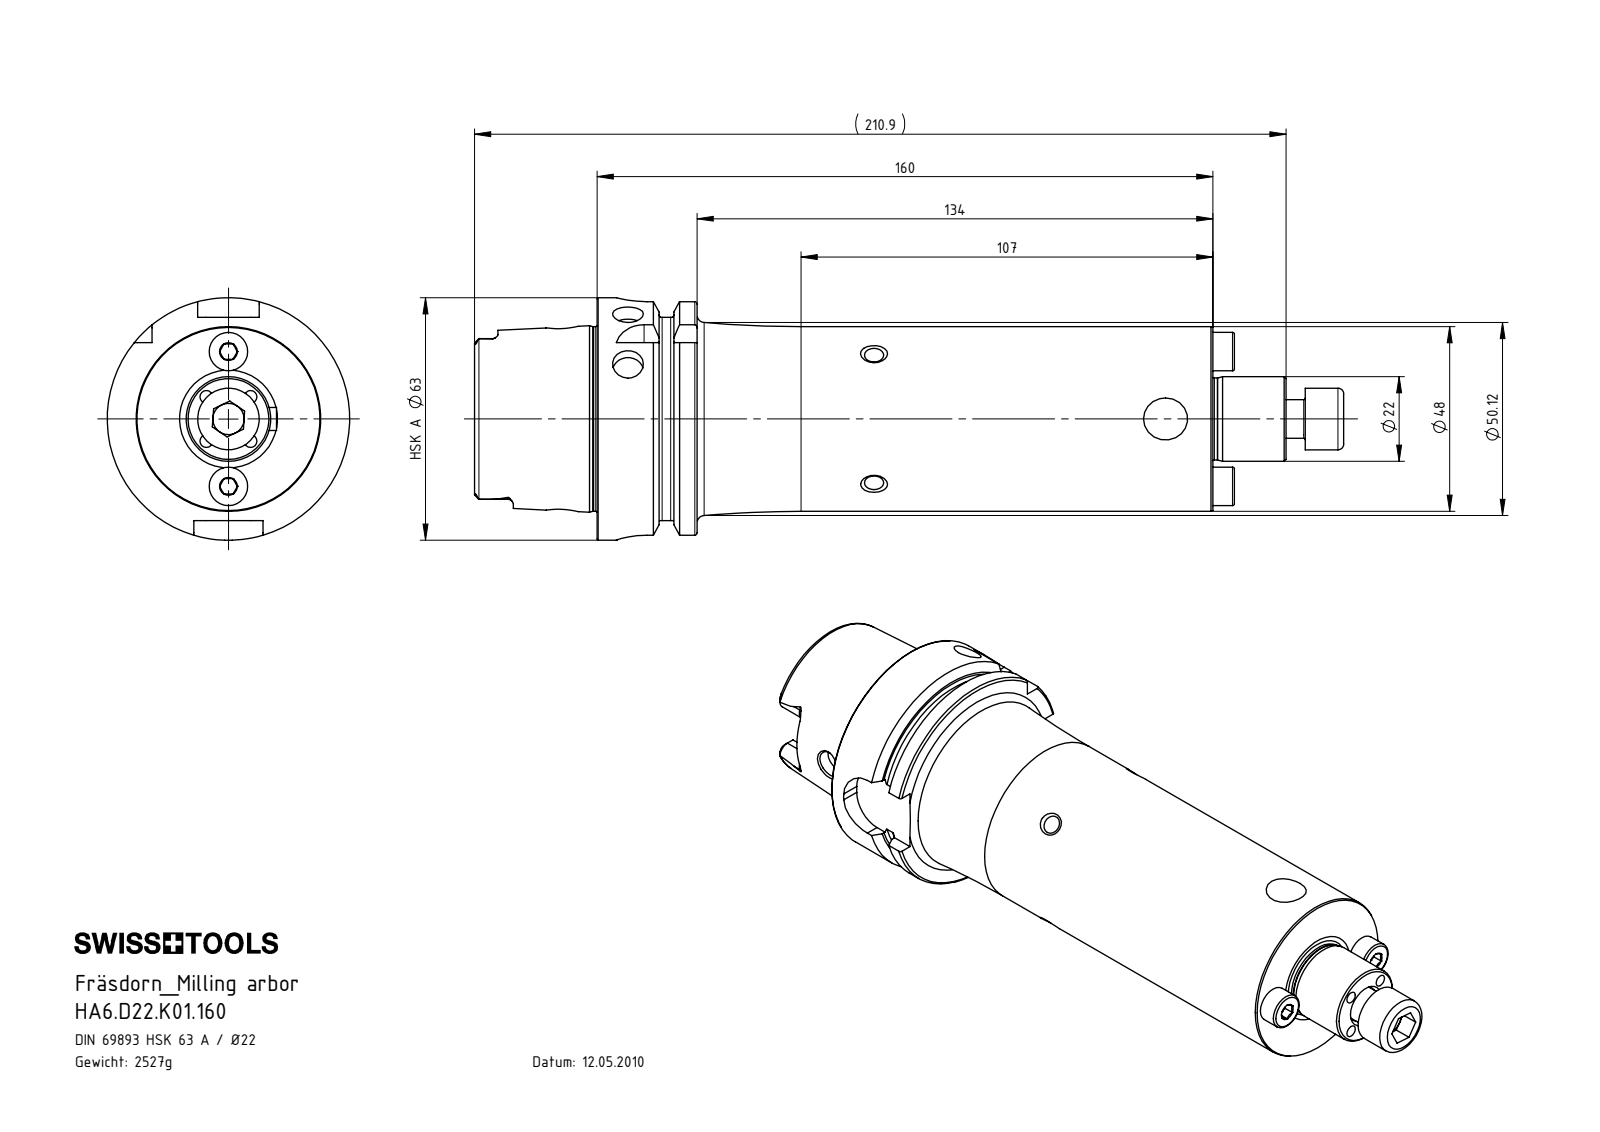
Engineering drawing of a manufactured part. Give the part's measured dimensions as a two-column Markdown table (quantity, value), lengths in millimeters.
| quantity | value |
| --- | --- |
| part name | DIN 6885 - 6x6x14; D22-ER2.001.017_B; HA6.D22.K01.160; ISO 4762 - M10 x 25 (+1 more) |
| STEP written by | SolidWorks 2017 (AUTOMOTIVE_DESIGN) |
| units | millimeters |
| bodies | 5 solids, 395 faces (96 planar, 116 cylindrical, 183 other) |
| overall size | 225.9 × 63 × 63 |
| volume | 325 069 mm³ |
| surface area | 54 256 mm² |
| round holes (diameter × count) | 3.3 × 6, 5 × 4, 8 × 4, 4.2 × 2, 7.5 × 1, 8.5 × 1, 10 × 1, 10.5 × 1, 17 × 1, 19 × 1, 34 × 1, 40 × 1 |
| round bosses / shafts (diameter × count) | 10 × 3, 5 × 2, 3.8 × 2, 63 × 1, 54.95 × 1, 48 × 1, 47.94 × 1, 22 × 1 |
| partial cylindrical surfaces (radius × count) | 1.4 × 6, 2.88 × 4, 3 × 4, 8 × 4 |
| main face-to-face distances | 160, 25.95, 134.05, 16, 150.05, 9.95, 31.9, 41.85, 57.85, 191.9 |
| hole center spacings | 8.13, 11.5, 13.08, 23.95, 79.05, 16.26, 17.5, 35 |
